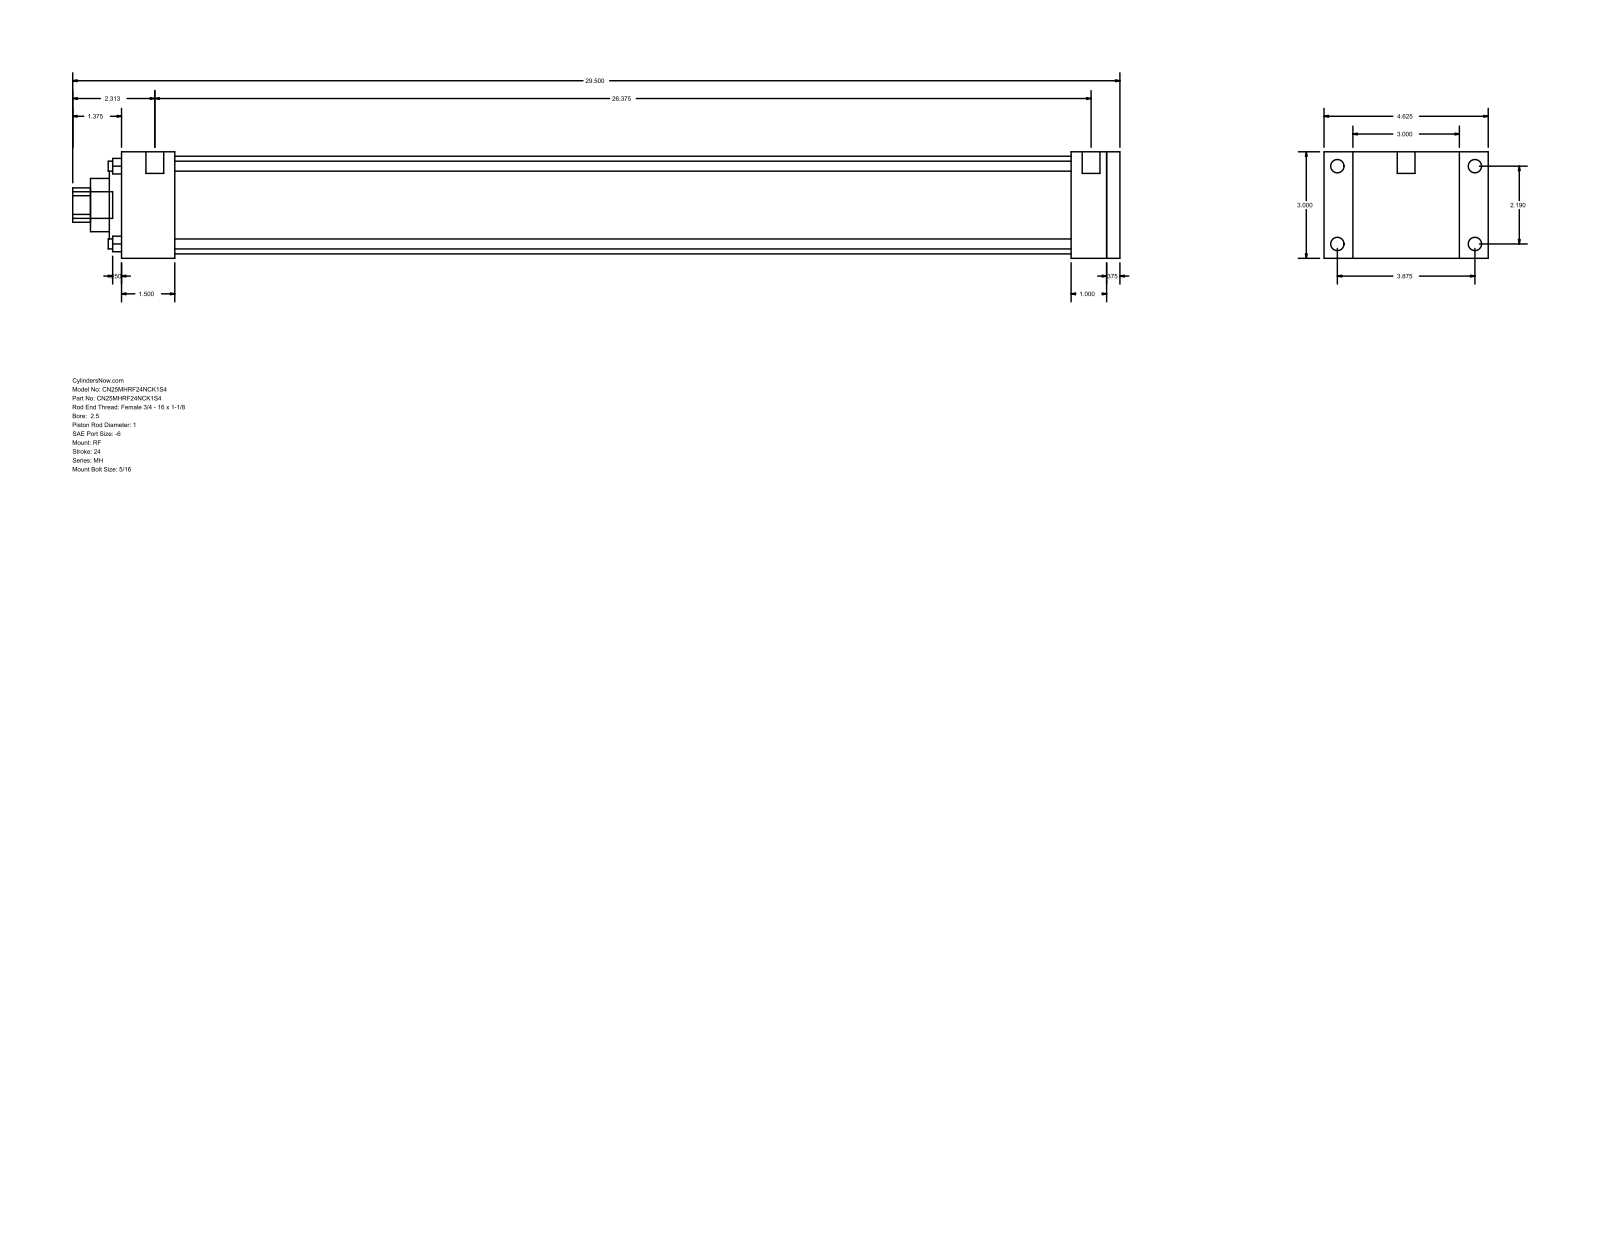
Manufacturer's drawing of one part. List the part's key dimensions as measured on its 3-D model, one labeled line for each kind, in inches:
Part name (STEP PRODUCT): MH_RF__0250_1
STEP written by: GSSL Pune (CONFIG_CONTROL_DESIGN)
Units: inches
Bodies: 0 solids, 94 faces (65 planar, 29 cylindrical, 0 other)
Overall size (bounding box): 29.5 × 4.625 × 3
Round holes (diameter × count): ⌀0.281 ×4, ⌀1 ×1, ⌀1.5 ×1, ⌀2.375 ×1, ⌀2.75 ×1
Round bosses / shafts (diameter × count): ⌀0.375 ×4, ⌀0.219 ×4, ⌀0.5 ×2, ⌀0.75 ×1
Partial cylindrical surfaces — rounded edges, fillets, slot ends (radius × count): R0.484 ×1
Main face-to-face distances: 3, 0.375, 28.125, 27.75, 1.375, 1, 26.75, 1.5, 25.25, 26.25
Hole centre spacings: 1.548, 2.19, 3.097
